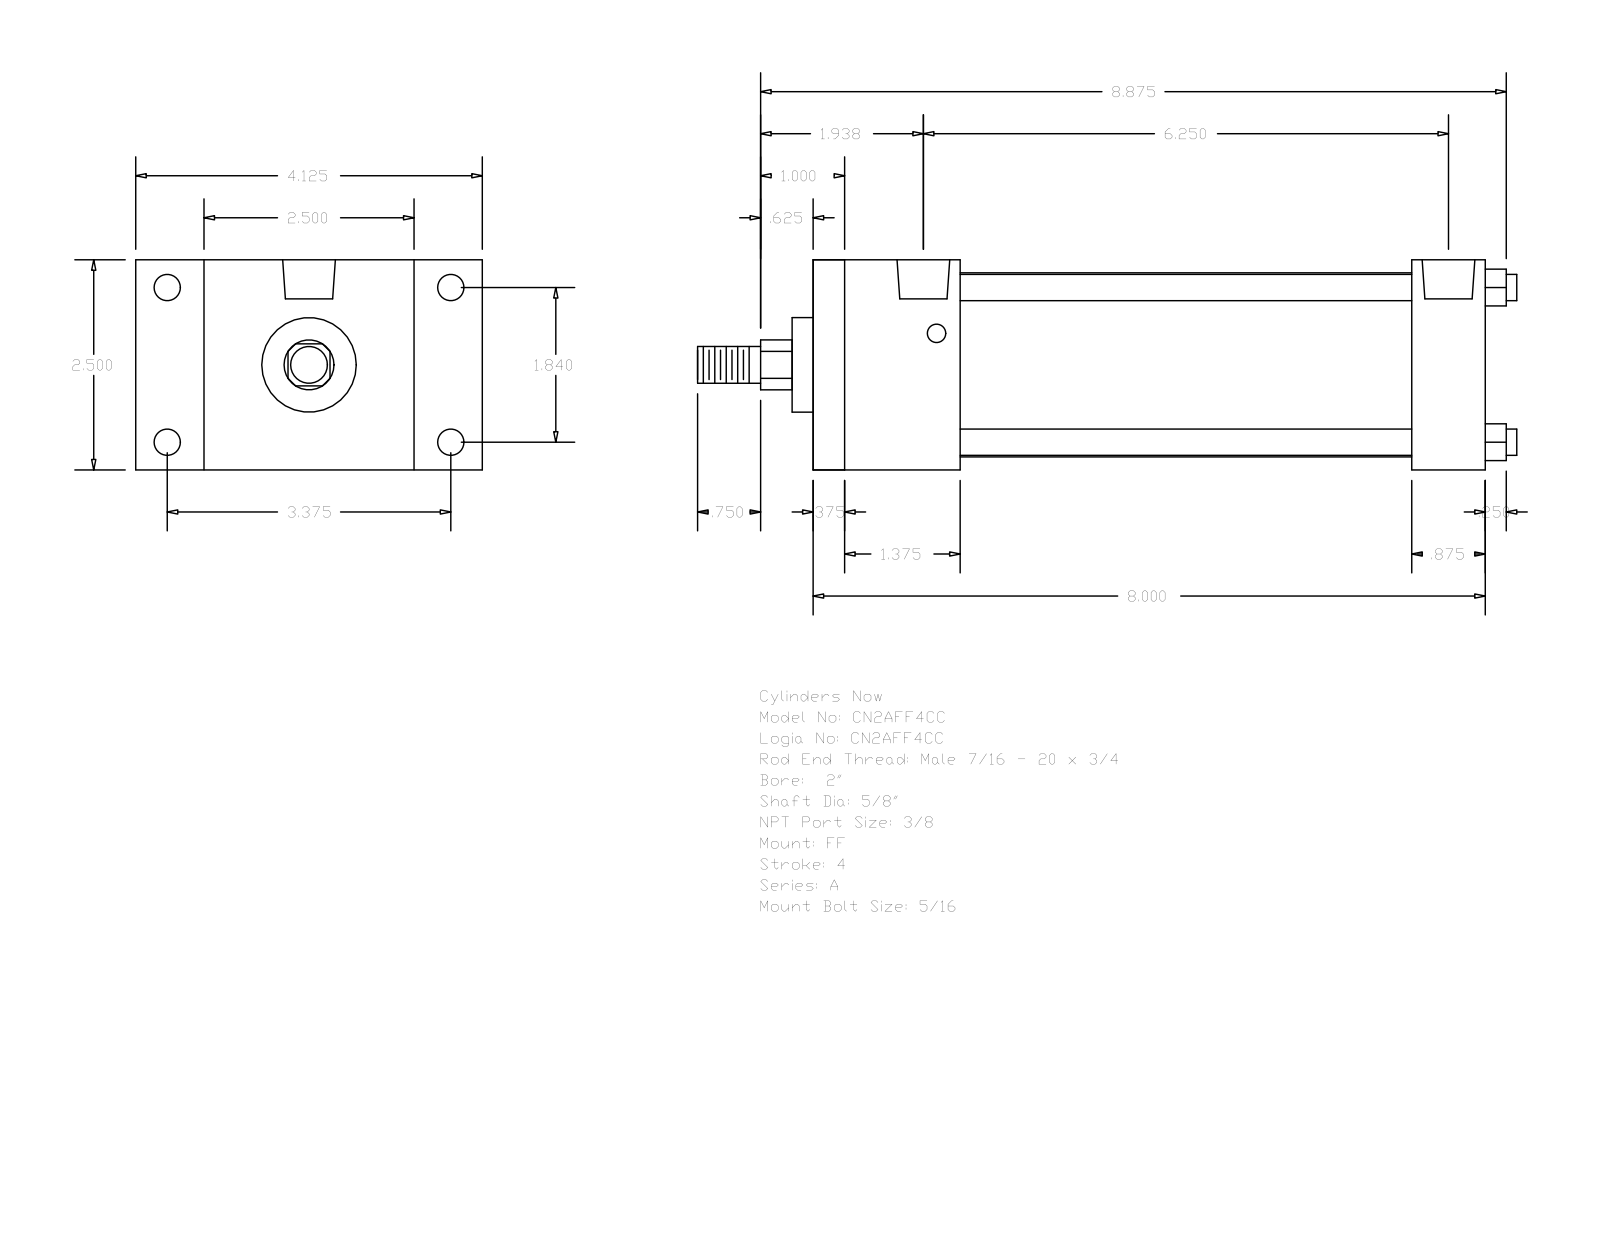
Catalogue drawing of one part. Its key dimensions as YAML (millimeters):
part_name: "A_FF__0200_0.625"
step_written_by: "GSSL Pune (CONFIG_CONTROL_DESIGN)"
units: millimeters
bodies: {solids: 0, faces: 92, planar: 64, cylindrical: 28, other: 0}
overall_size: [247.65, 104.78, 63.5]
round_holes:
  - {diameter: 5.56, count: 4}
  - {diameter: 7.94, count: 4}
  - {diameter: 15.93, count: 2}
round_bosses_or_shafts:
  - {diameter: 7.94, count: 4}
  - {diameter: 55.63, count: 1}
  - {diameter: 28.57, count: 1}
  - {diameter: 15.88, count: 1}
  - {diameter: 11.11, count: 1}
partial_cylinders:
  - {radius: 7.54, count: 1}
face_to_face_distances: [63.5, 203.19, 9.52, 193.67, 34.93, 44.45, 180.97, 171.45, 136.52, 158.74]
hole_center_spacings: [46.74, 85.72, 97.63, 150.8, 3.97, 3.98, 154.77, 154.78]
